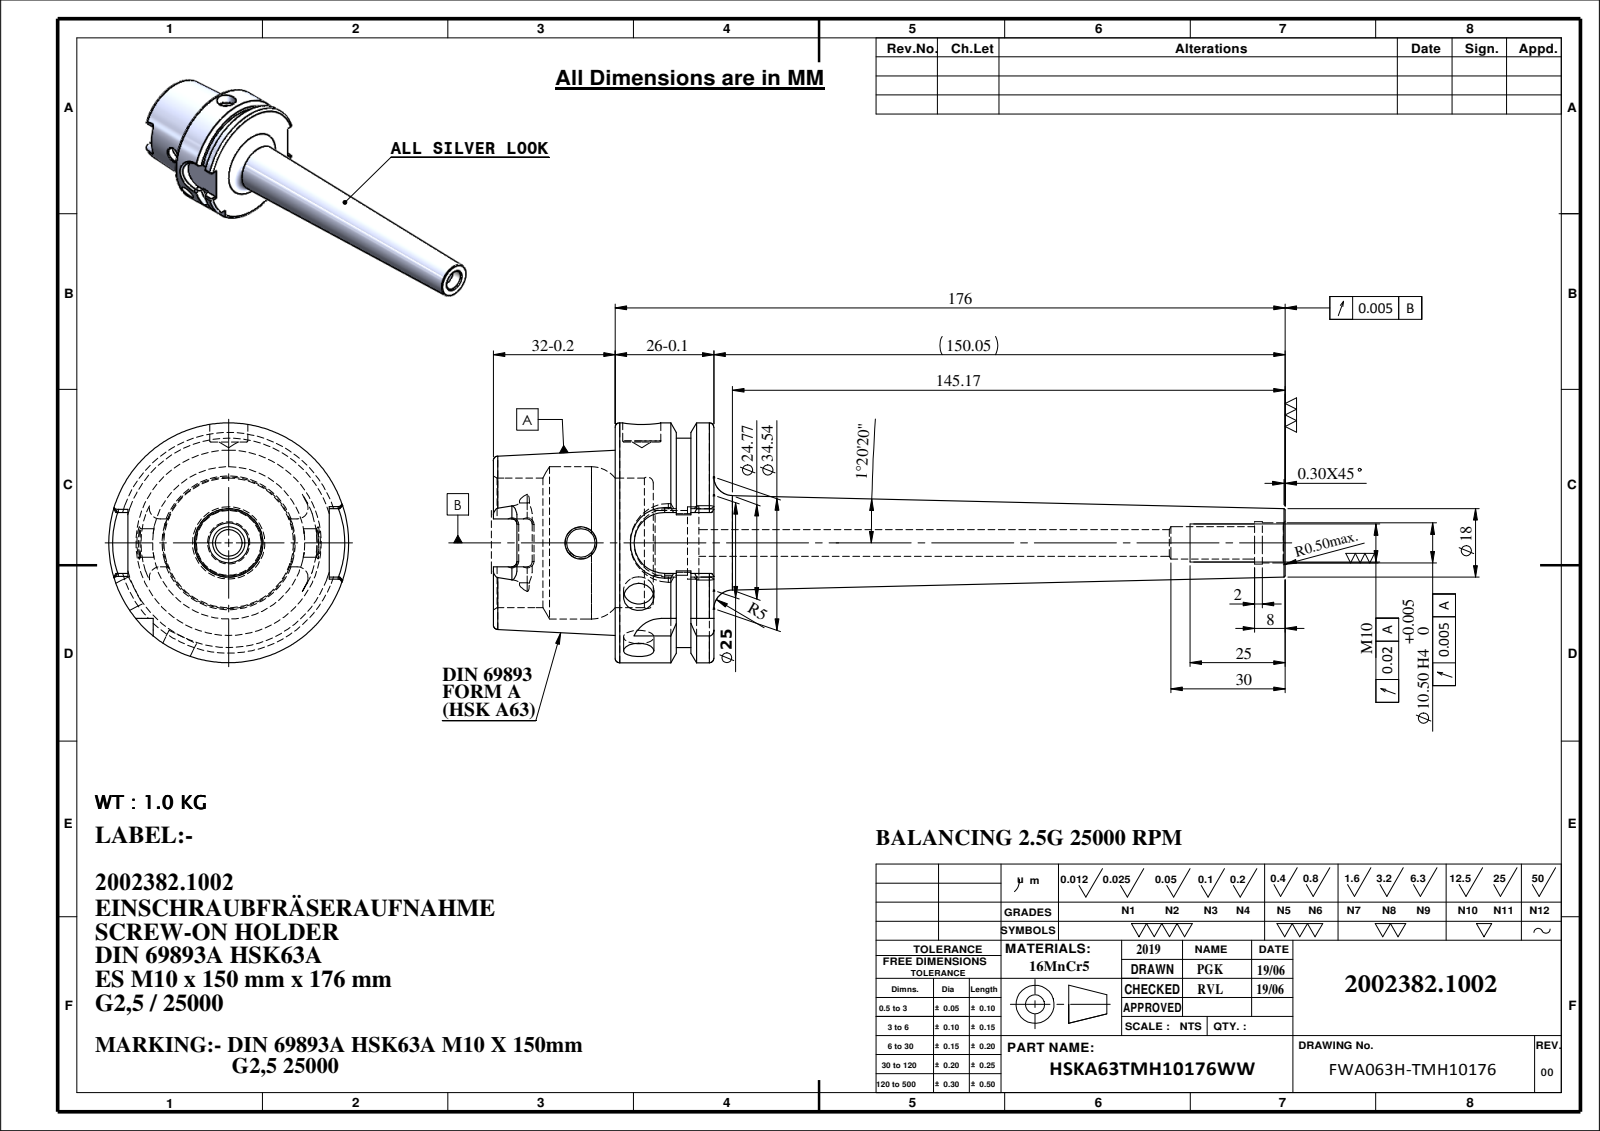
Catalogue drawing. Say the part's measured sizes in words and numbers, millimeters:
The part is named "9163A-ES8M10150; HSKA63TMH10176WW-FIN". Its 3-D file was written by "SolidWorks 2018 (CONFIG_CONTROL_DESIGN)". It is 1 solid with 168 faces: 51 planar, 51 cylindrical and 66 other. Overall it measures 208 by 63 by 63 millimeters. Its volume is 129 644 cubic millimeters and its surface area 35 596 square millimeters. Round holes: 2 of diameter 8, 1 of diameter 7, 1 of diameter 7.5, 1 of diameter 8.5, 1 of diameter 10, 1 of diameter 10.5, 1 of diameter 11.1, 1 of diameter 17, 1 of diameter 19, 1 of diameter 34, 1 of diameter 40. Round bosses or shafts: 1 of diameter 63, 1 of diameter 55. Partial cylindrical surfaces (rounded edges, fillets, slot ends): 6 of radius 1.3, 4 of radius 2.88, 2 of radius 8, 1 of radius 9. The main face-to-face distances are 25.95, 10, 15.95, 32, 42, 57.95, 52.9, 54, 22, 12.
